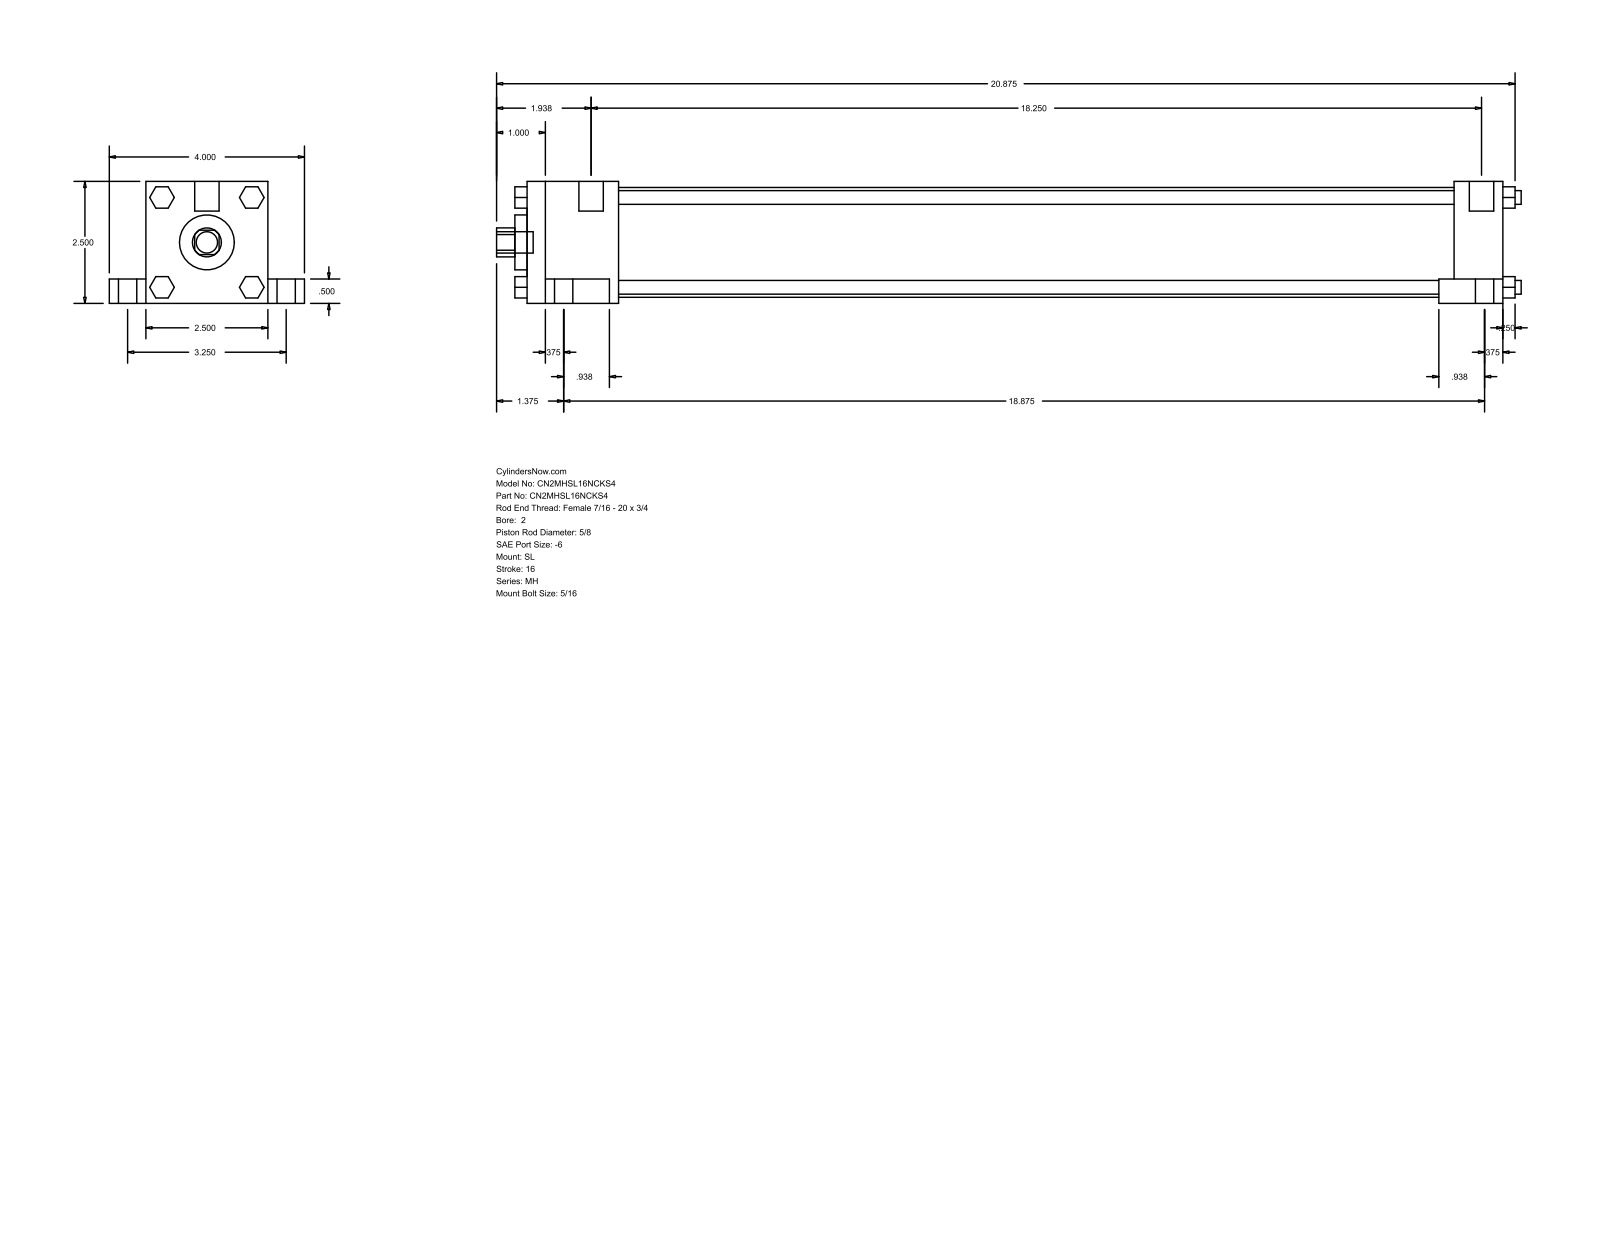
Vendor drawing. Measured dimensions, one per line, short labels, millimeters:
name: MH_SL__0200_0.625
written by: GSSL Pune (CONFIG_CONTROL_DESIGN)
unit: mm
bodies: 0 solids, 148 faces (112 planar, 36 cylindrical, 0 other)
size: 533.4 × 101.6 × 63.5
holes: 1× ⌀15.88, 1× ⌀28.57, 1× ⌀57.15
bosses: 4× ⌀15.88, 4× ⌀9.53, 4× ⌀7.14, 4× ⌀5.56, 2× ⌀12.7, 1× ⌀11.11
rounds: 1× R7.54
face distances: 63.5, 508, 12.7, 19.05, 50.8, 82.55, 25.4, 482.6, 47.62, 434.98
